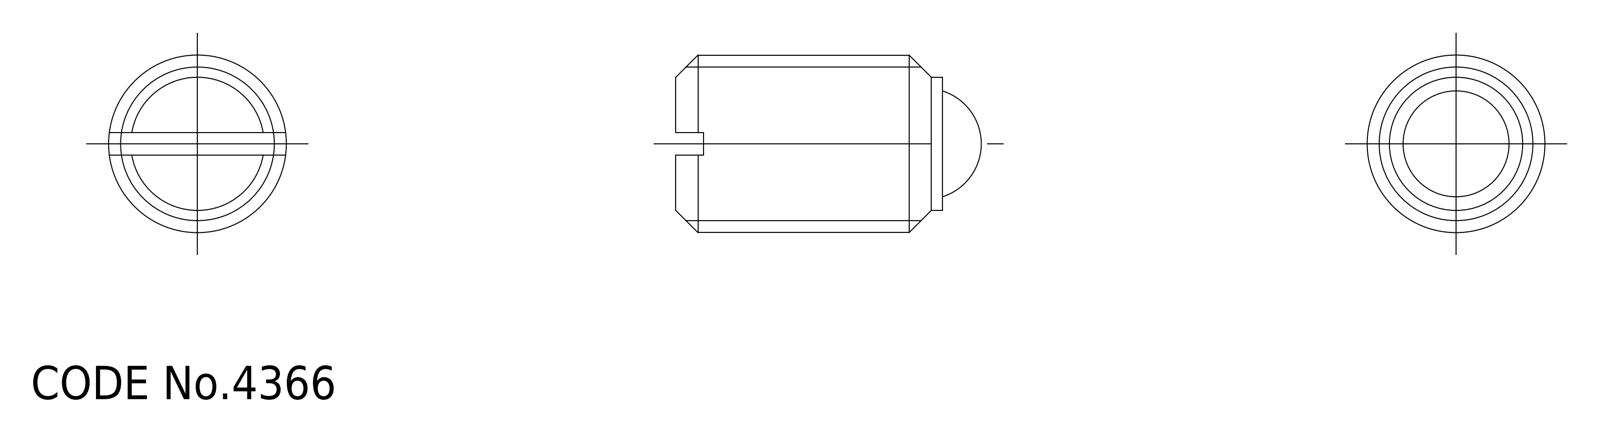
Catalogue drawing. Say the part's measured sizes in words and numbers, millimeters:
The part is named "ball; PBF_16_14008_36". Its 3-D file was written by "CADfix (AUTOMOTIVE_DESIGN)". It is 2 solids with 19 faces: 0 planar, 0 cylindrical and 19 other. Overall it measures 27.5 by 16 by 16 millimeters. Its volume is 4 113 cubic millimeters and its surface area 2 210 square millimeters.
